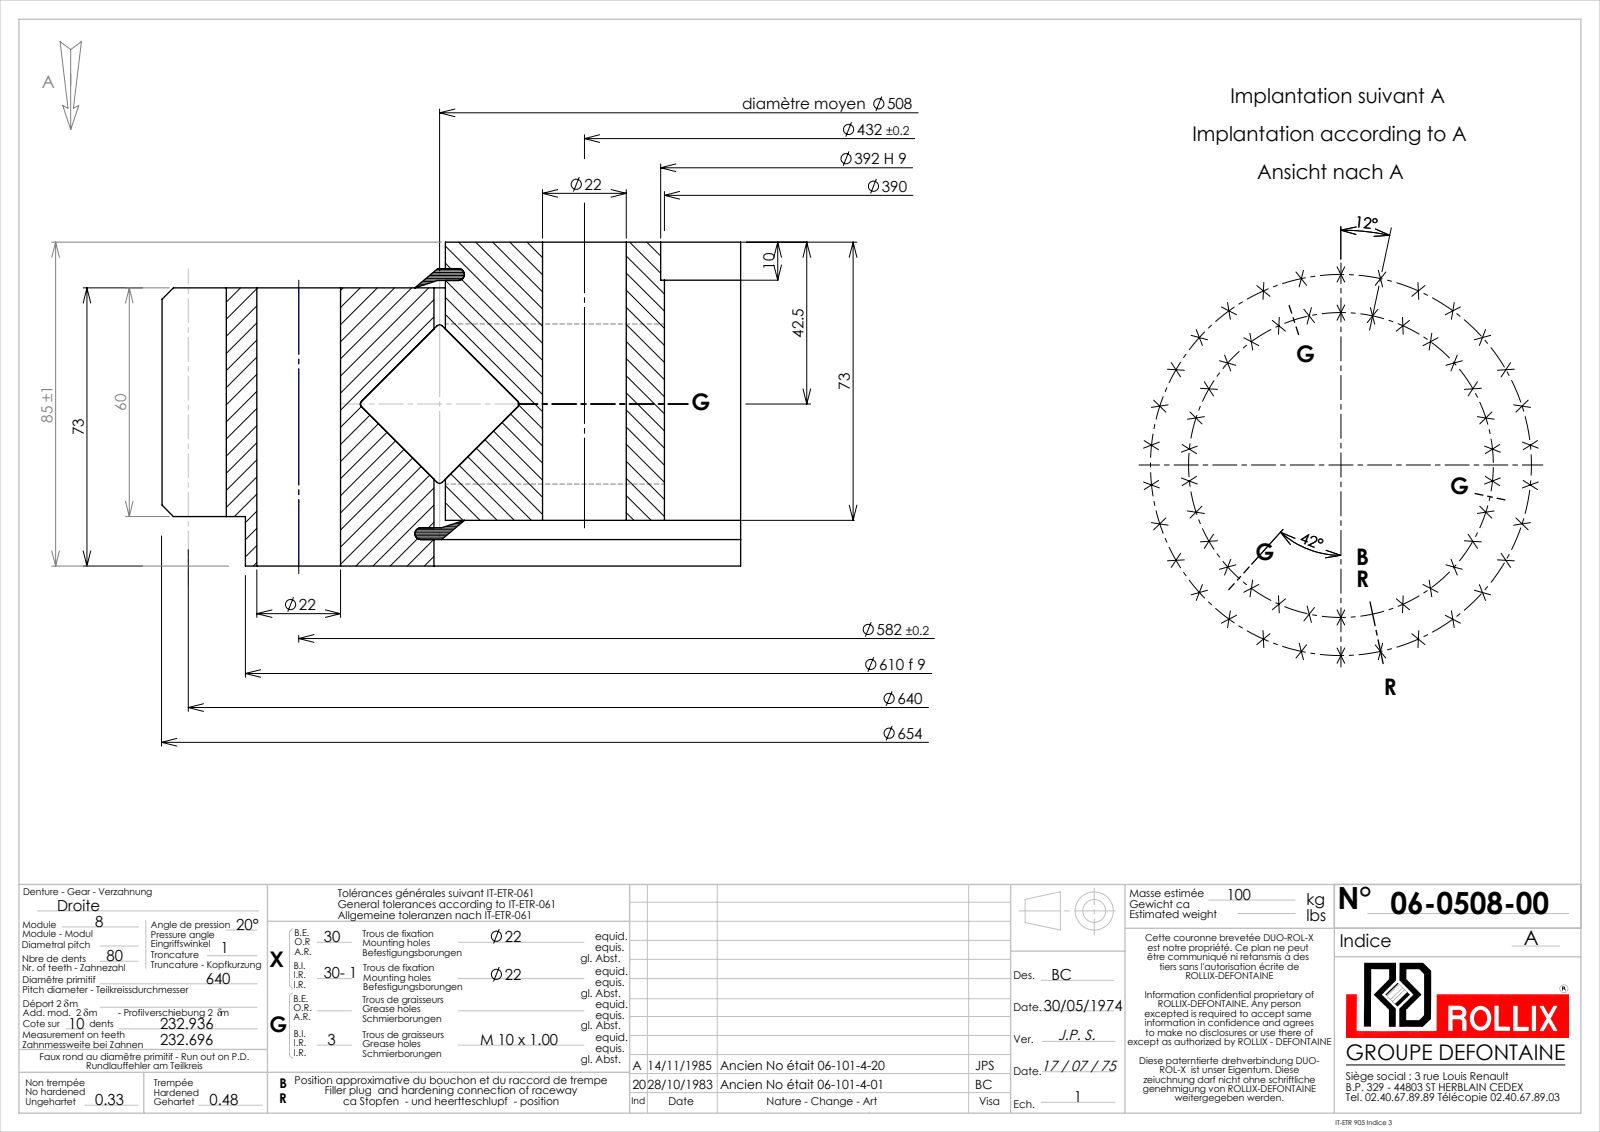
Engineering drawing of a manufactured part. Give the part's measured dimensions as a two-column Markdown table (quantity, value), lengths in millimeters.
| quantity | value |
| --- | --- |
| part name | 06-0508-00 |
| STEP written by | SolidWorks 2016 (CONFIG_CONTROL_DESIGN) |
| units | millimeters |
| bodies | 5 solids, 683 faces (176 planar, 305 cylindrical, 202 other) |
| overall size | 653.76 × 653.76 × 85 |
| volume | 11 120 000 mm³ |
| surface area | 1 407 000 mm² |
| round holes (diameter × count) | 22 × 59, 9 × 3, 390 × 1, 392 × 1, 511 × 1 |
| round bosses / shafts (diameter × count) | 610 × 1, 505 × 1, 30 × 1 |
| partial cylindrical surfaces (radius × count) | 310 × 1, 327 × 1 |
| main face-to-face distances | 73, 12, 61, 85, 6.95, 78.05, 5.05, 66.05, 10.05, 74.95 |
| hole center spacings | 432.51, 470.85, 236.72, 291, 179.85, 342.09, 578.81, 121 |
